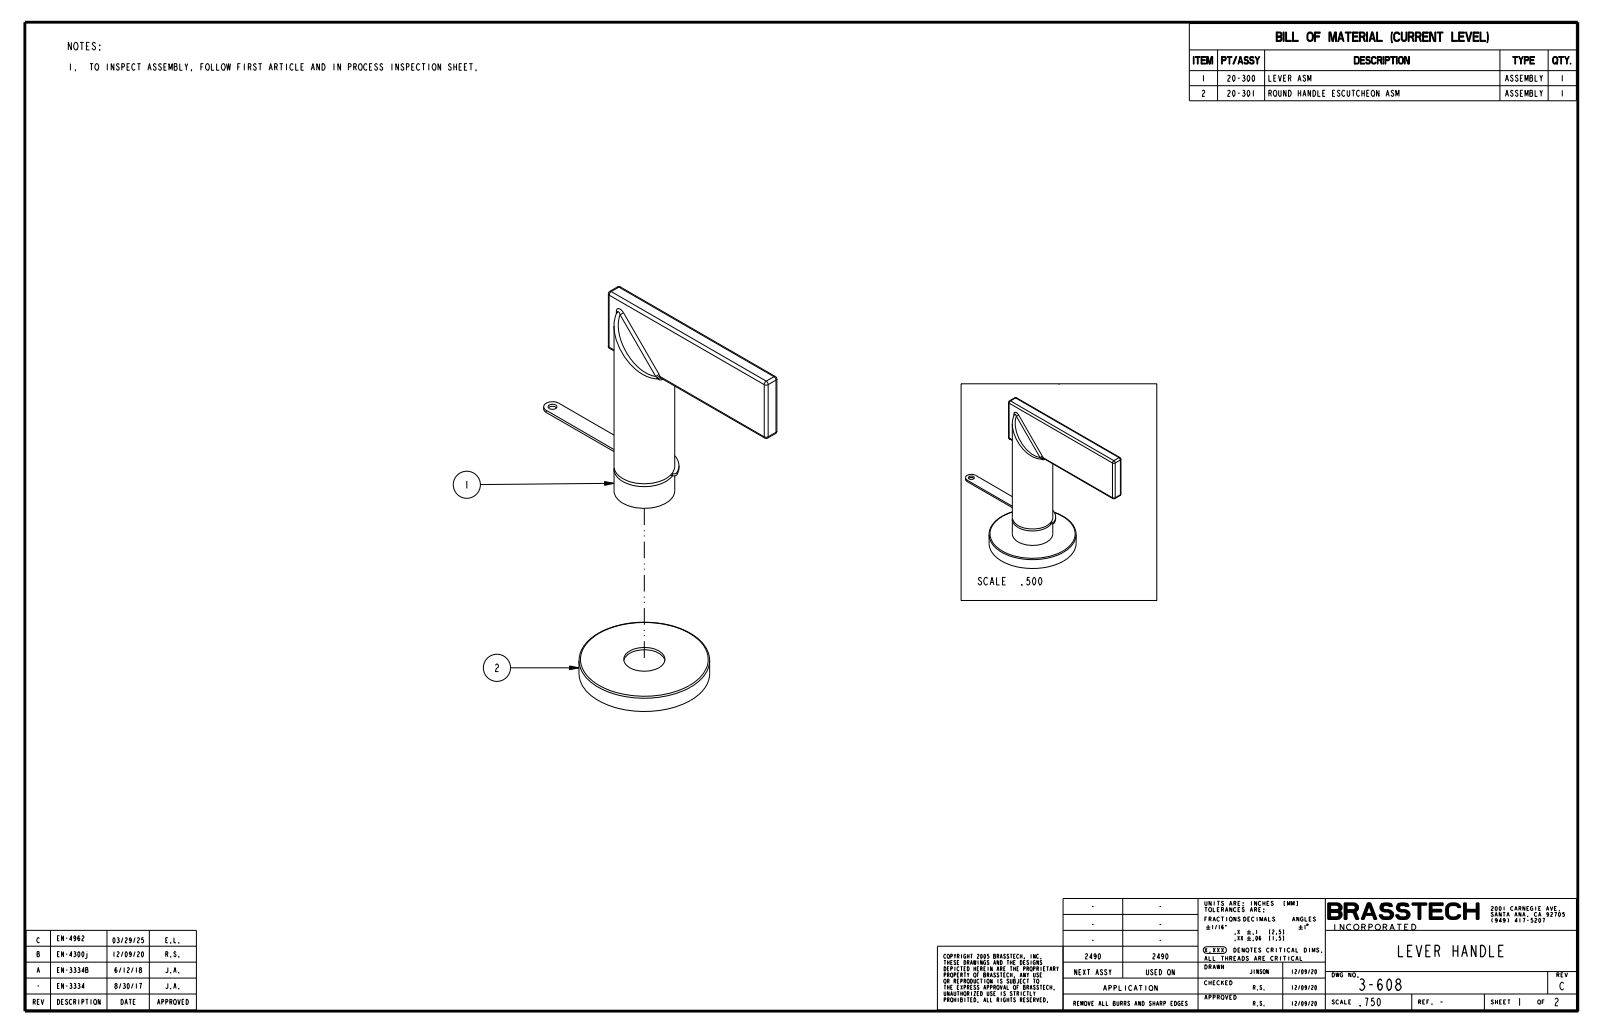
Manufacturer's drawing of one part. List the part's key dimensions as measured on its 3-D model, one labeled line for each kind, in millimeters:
Part name (STEP PRODUCT): 3-608
STEP written by: CREO PARAMETRIC BY PTC INC, 2018400 (CONFIG_CONTROL_DESIGN)
Units: millimetres
Bodies: 1 solid, 63 faces (13 planar, 26 cylindrical, 24 other)
Overall size (bounding box): 88.5 × 87.6 × 47
Volume: 46 590 mm³ · Surface area: 13 550 mm²
Round bosses / shafts (diameter × count): ⌀47 ×1, ⌀21.8 ×1, ⌀17.3 ×1
Partial cylindrical surfaces — rounded edges, fillets, slot ends (radius × count): R1 ×16
Main face-to-face distances: 6, 6.4, 87.6, 81.3, 62.6, 56.3, 25, 15.9, 9.6, 46.7
